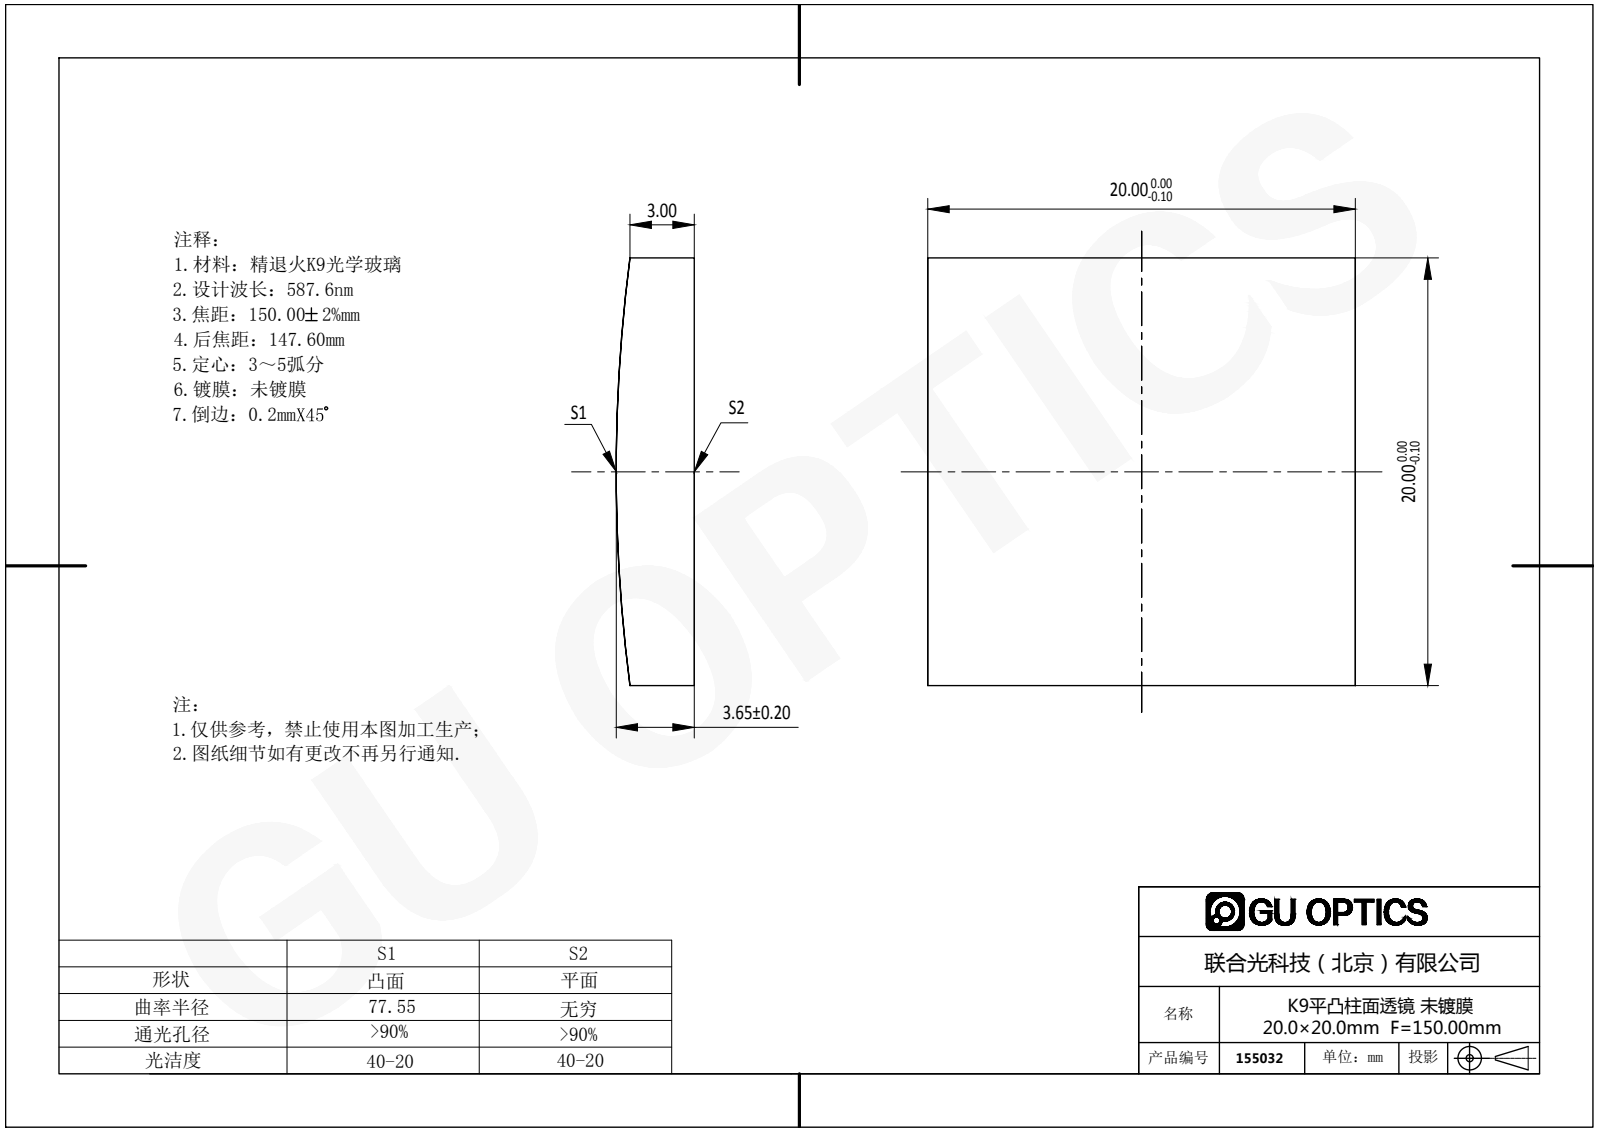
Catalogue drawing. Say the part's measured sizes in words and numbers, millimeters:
The part is named "155032". Its 3-D file was written by "SolidWorks 2016 (AUTOMOTIVE_DESIGN)". It is 1 solid with 6 faces: 5 planar, 1 cylindrical and 0 other. Overall it measures 20 by 20 by 3.65 millimeters. Its volume is 1 374 cubic millimeters and its surface area 1 059 square millimeters. Partial cylindrical surfaces (rounded edges, fillets, slot ends): 1 of radius 77.55. The main face-to-face distances are 20.
